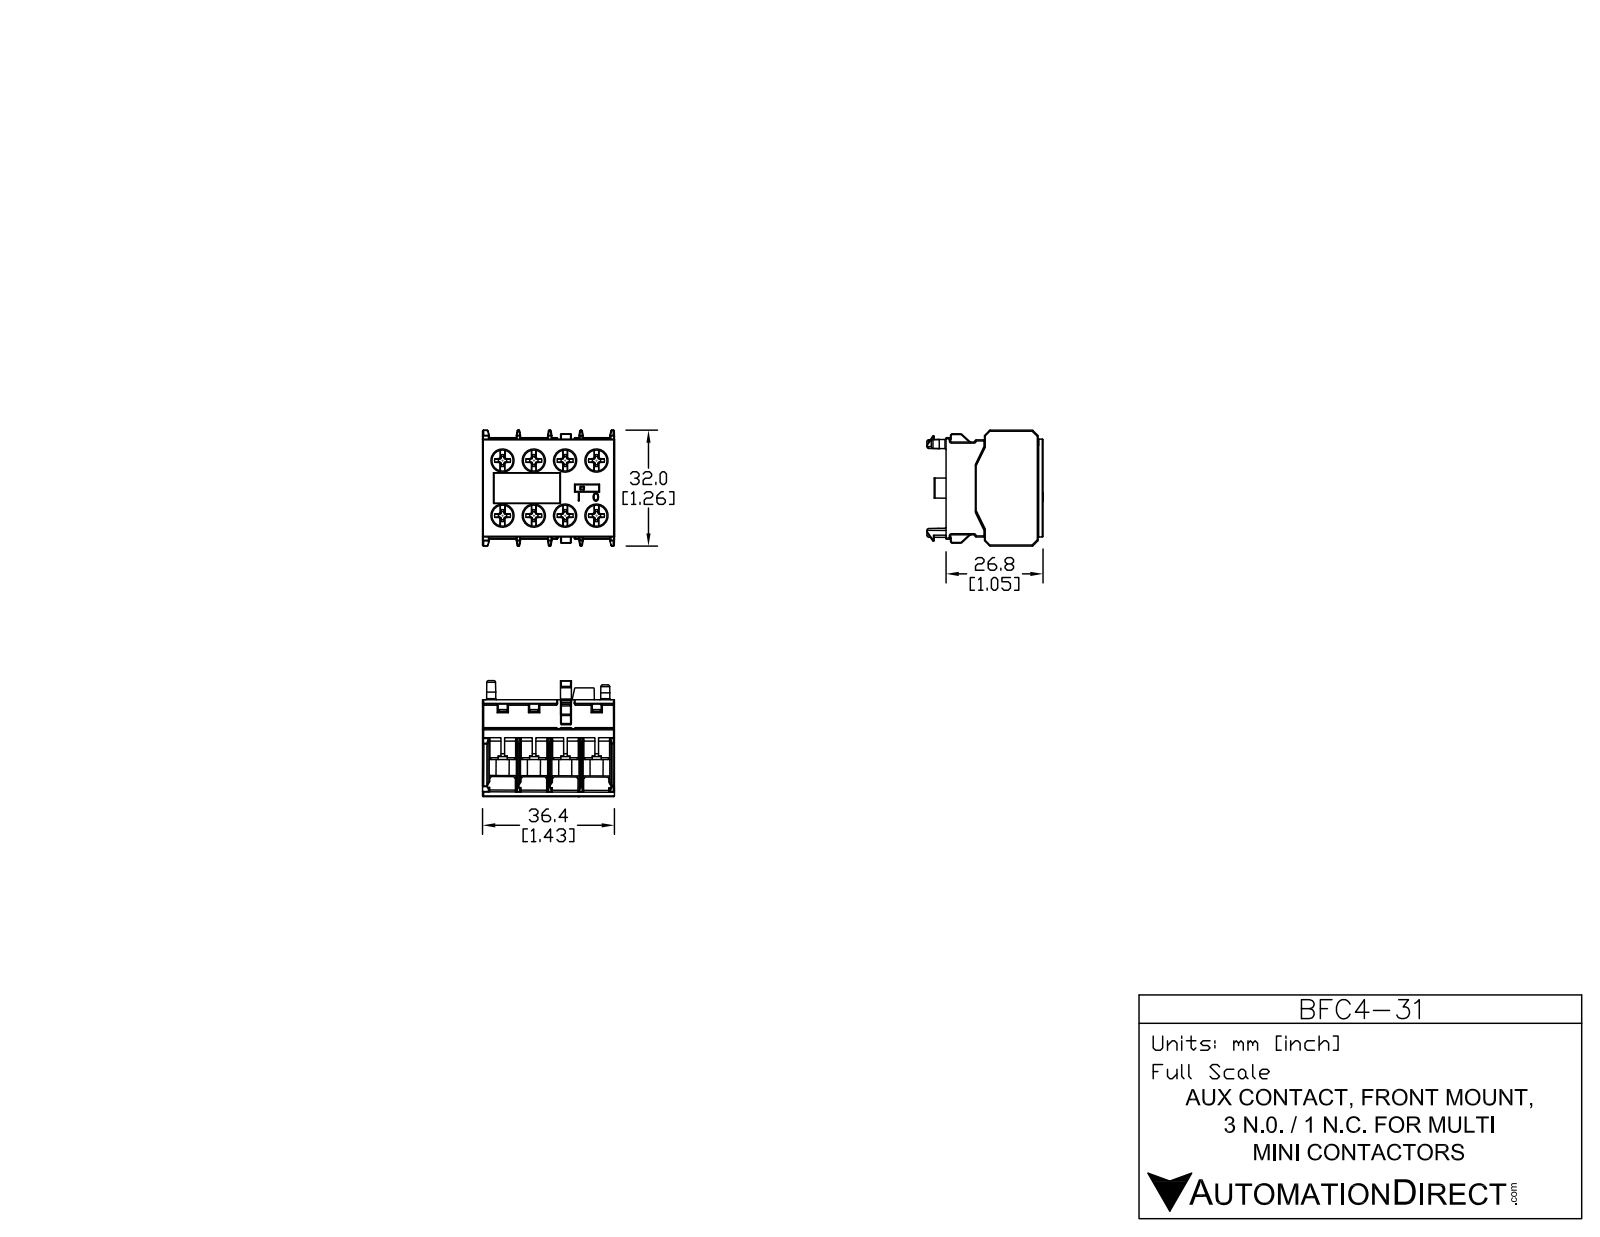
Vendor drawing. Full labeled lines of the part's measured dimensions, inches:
Part name (STEP PRODUCT): BFC4-31
STEP written by: SolidWorks 2013 (AUTOMOTIVE_DESIGN)
Units: inches
Bodies: 20 solids, 761 faces (593 planar, 168 cylindrical, 0 other)
Overall size (bounding box): 1.437 × 1.269 × 1.26
Volume: 1.002 in³ · Surface area: 26.95 in²
Round holes (diameter × count): ⌀0.236 ×8
Round bosses / shafts (diameter × count): ⌀0.197 ×8, ⌀0.118 ×8, ⌀0.108 ×3
Partial cylindrical surfaces — rounded edges, fillets, slot ends (radius × count): R0.02 ×8, R0.178 ×8, R0.012 ×6, R0.01 ×4, R0.006 ×2, R0.007 ×2, R0.008 ×2
Main face-to-face distances: 0.049, 0.679, 0.34, 0.63, 0.339, 1.019, 0.291, 0.728, 0.389, 0.29
Hole centre spacings: 0.34, 0.591, 0.679, 0.681, 0.9, 0.339, 0.681, 1.019
